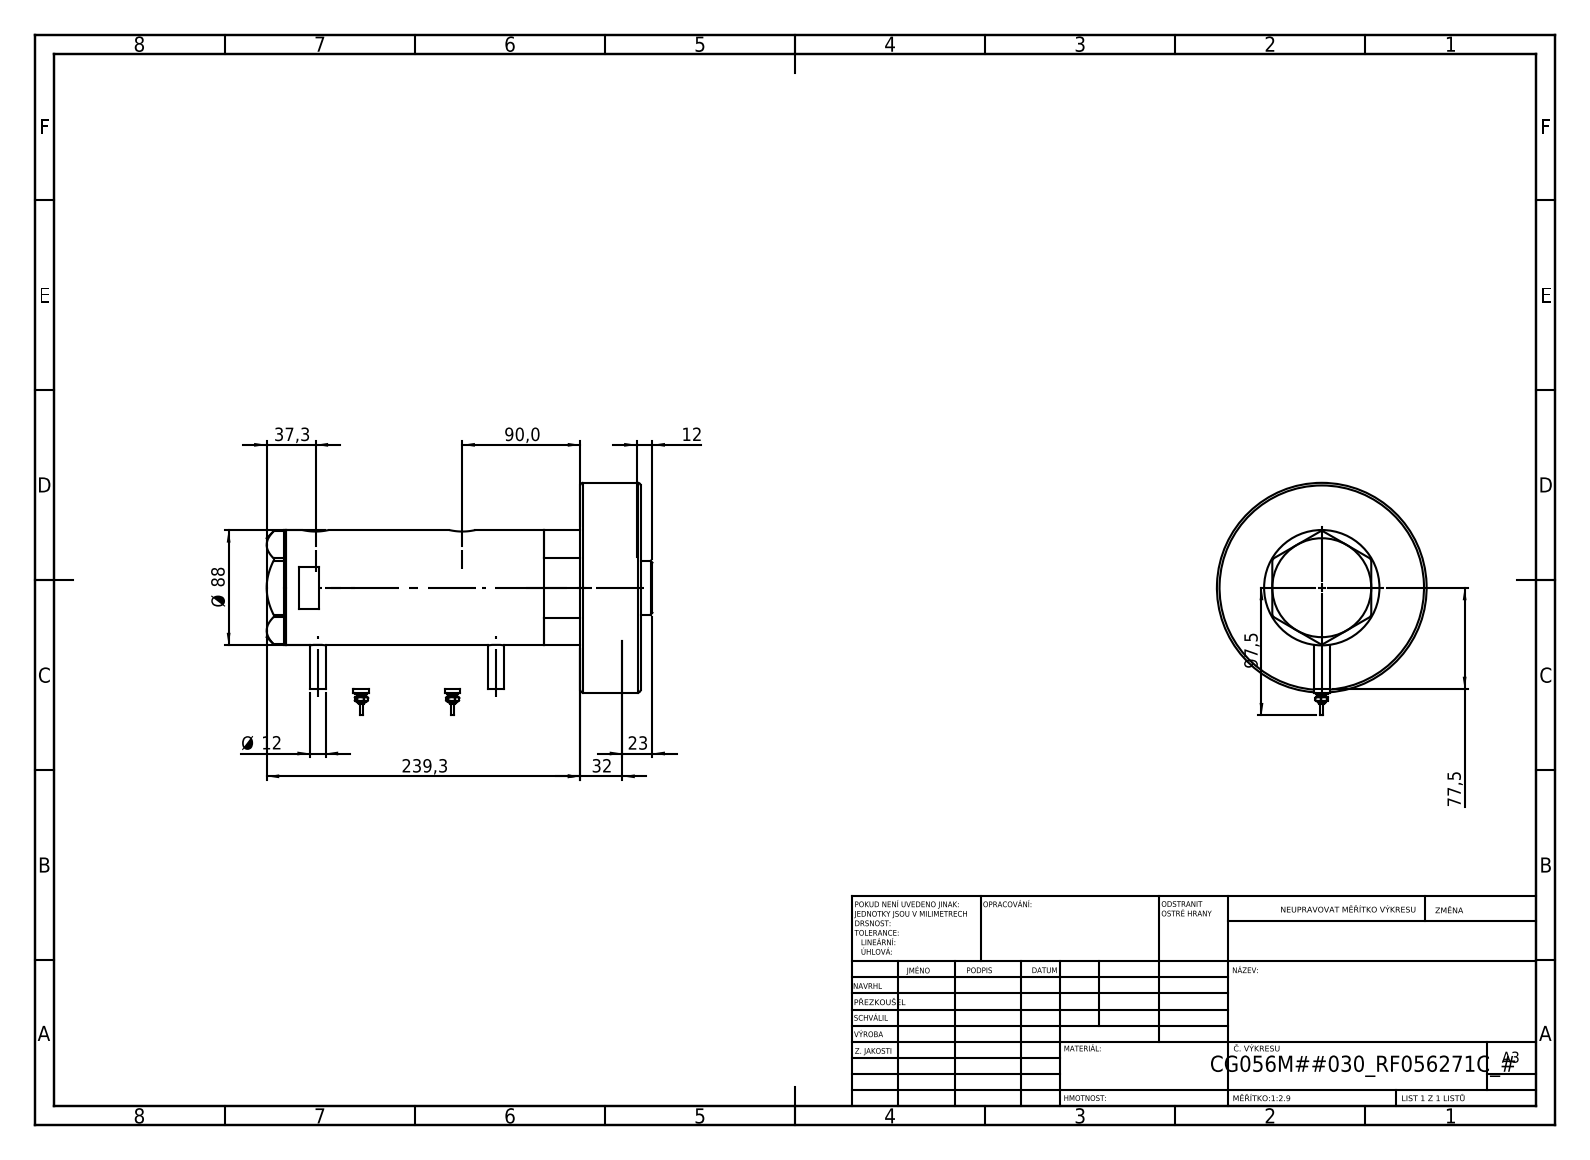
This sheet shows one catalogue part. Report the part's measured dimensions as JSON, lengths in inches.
{"part_name": "Switch; V270CG_271C; V270CG_FRONT; V270CG_BACK (+2 more)", "step_written_by": "SolidWorks 2019 (CONFIG_CONTROL_DESIGN)", "units": "inches", "bodies": {"solids": 7, "faces": 223, "planar": 82, "cylindrical": 73, "other": 68}, "overall_size": [11.587, 6.988, 6.299], "volume_in3": 139.4, "surface_area_in2": 449.4, "round_holes": [[0.492, 2], [0.518, 2], [0.787, 2], [0.571, 1], [1.654, 1], [1.713, 1], [2.205, 1], [2.362, 1], [2.953, 1], [3.15, 1]], "round_bosses_or_shafts": [[0.472, 4], [0.354, 2], [0.276, 2], [0.177, 2], [0.098, 2], [6.299, 1], [3.465, 1], [2.874, 1]], "face_to_face_distances": [1.811, 8.831, 10.642, 5.291, 3.539, 5.35, 9.618, 1.024, 4.268, 7.807], "hole_center_spacings": [0.067, 1.016, 4.343, 4.409, 5.358, 5.425]}
